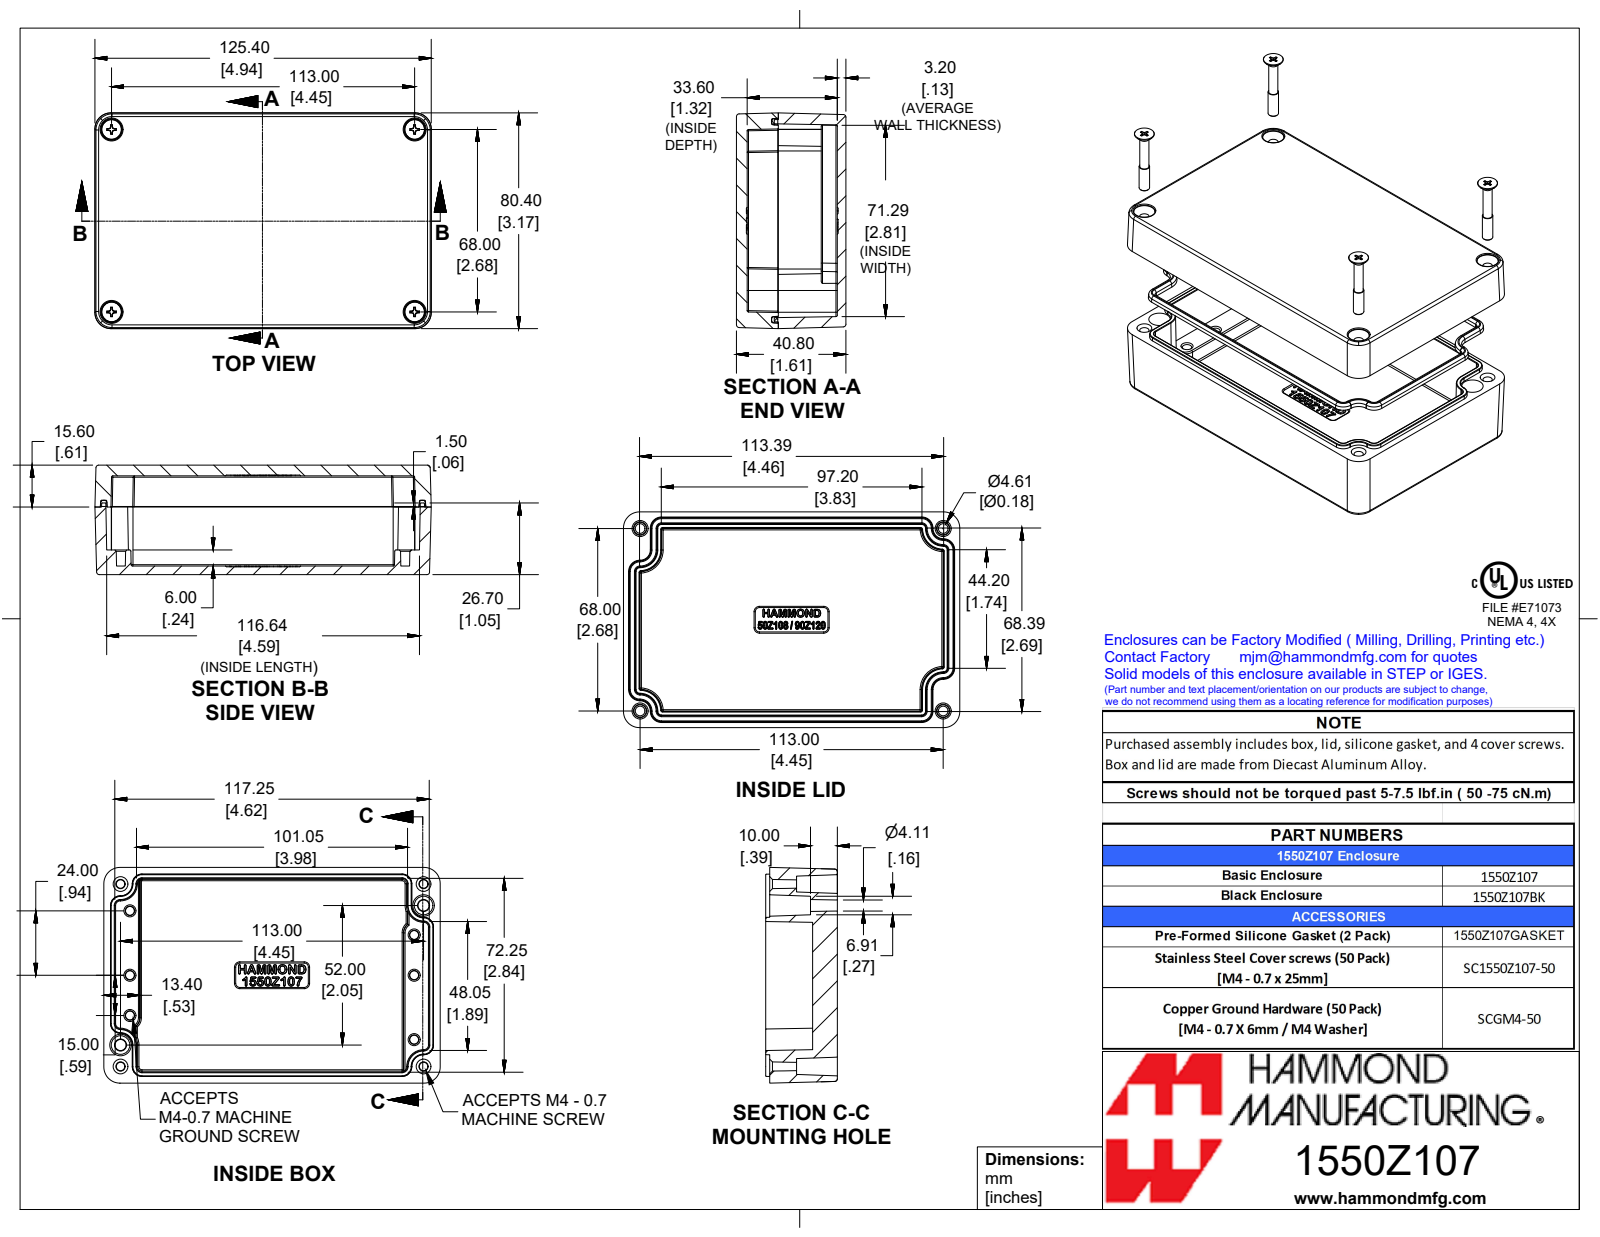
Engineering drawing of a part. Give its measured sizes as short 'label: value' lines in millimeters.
name: 1550Z107
written by: SolidWorks 2019 (AUTOMOTIVE_DESIGN)
unit: mm
bodies: 7 solids, 1416 faces (385 planar, 220 cylindrical, 811 other)
size: 125.4 × 80.4 × 40.8
volume: 144 900 mm³; area: 78 710 mm²
holes: 4× ⌀3.6
bosses: 4× ⌀7.6, 4× ⌀3.9, 4× ⌀3.3
rounds: 46× R0.2, 28× R0.5, 28× R1, 20× R0.3, 8× R6, 2× R4
face distances: 40.8, 36.8, 4, 3.2, 33.6, 37.6, 80.4, 11.6, 25.2, 22
hole spacings: 68, 113, 131.9
